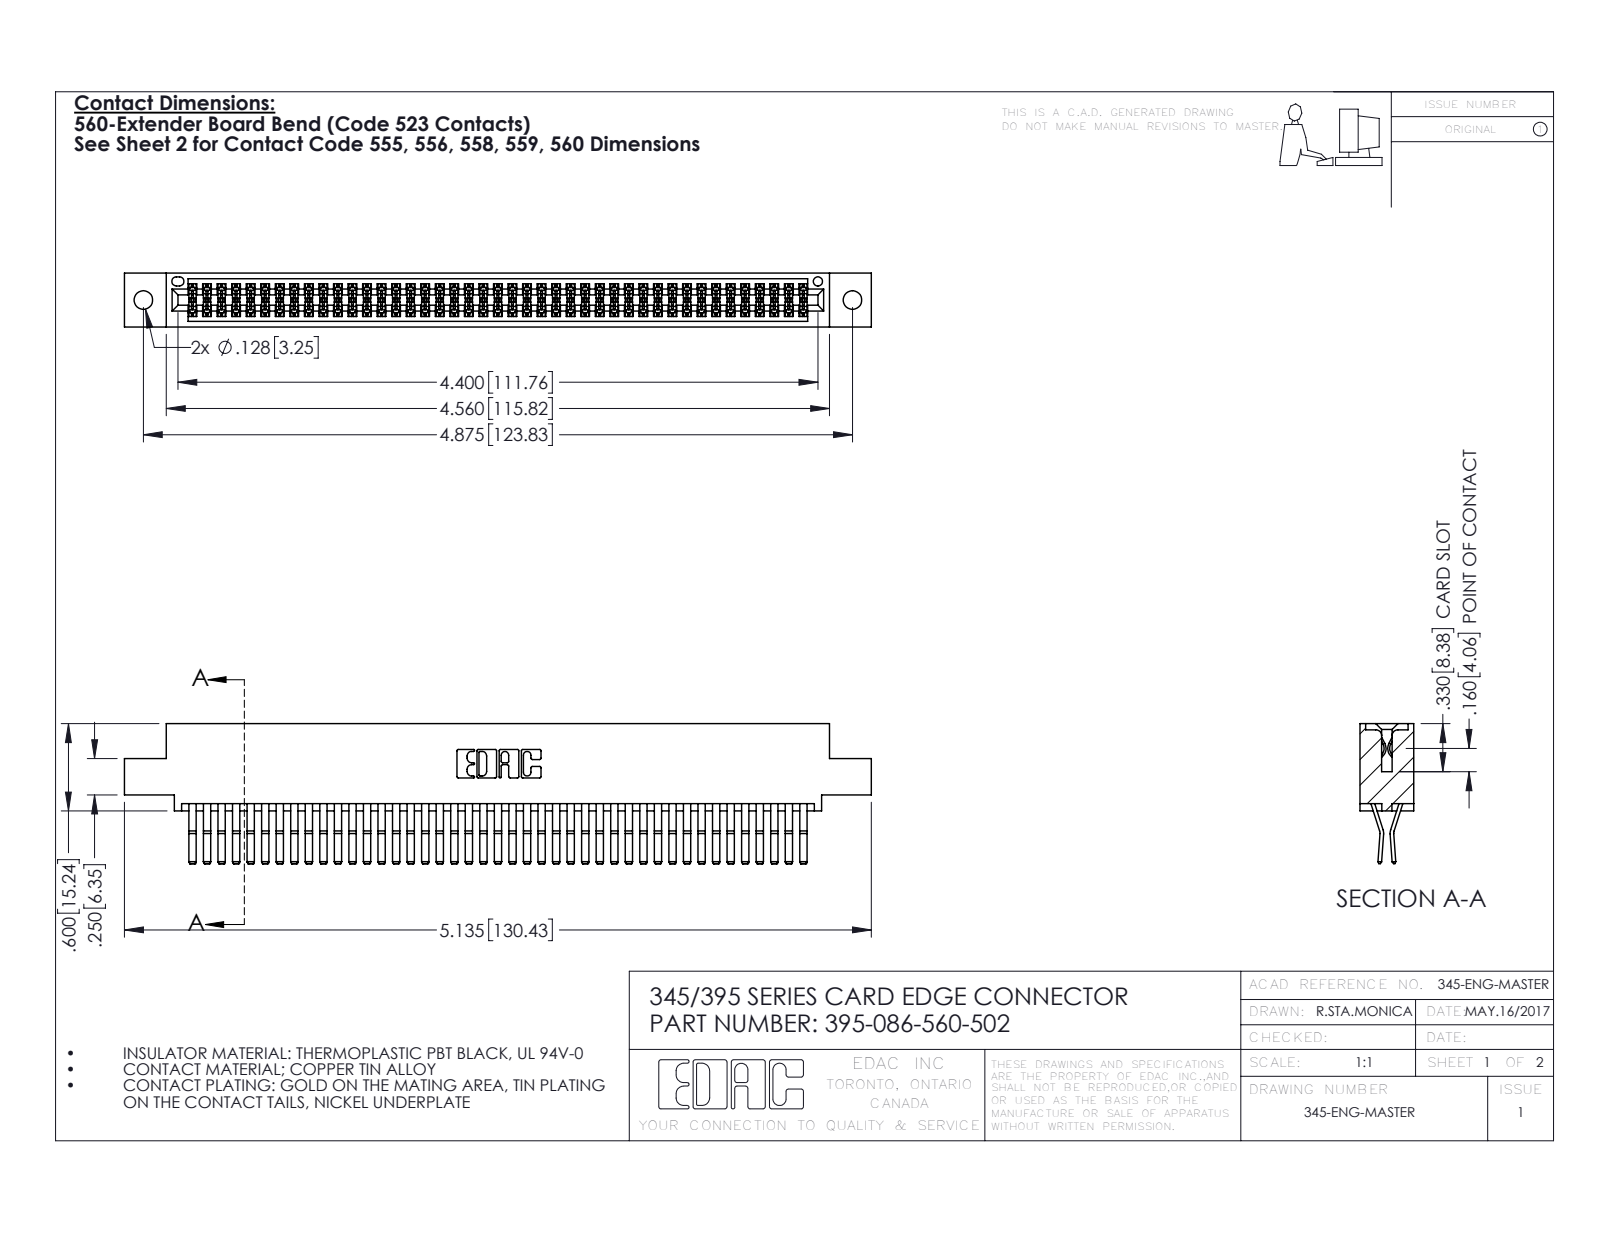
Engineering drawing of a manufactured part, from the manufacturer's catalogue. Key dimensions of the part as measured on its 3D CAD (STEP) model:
Part name (STEP PRODUCT): 395-086-560-502; 345-292-001_560 Tail; 345 Part_0.110 Offset - 0.128 Dia
STEP written by: SolidWorks 2016 (CONFIG_CONTROL_DESIGN)
Units: inches
Bodies: 87 solids, 4602 faces (2922 planar, 1680 cylindrical, 0 other)
Overall size (bounding box): 5.135 × 0.962 × 0.37
Volume: 0.801 in³ · Surface area: 32.09 in²
Round holes (diameter × count): ⌀0.128 ×2, ⌀0.064 ×1
Partial cylindrical surfaces — rounded edges, fillets, slot ends (radius × count): R0.006 ×130, R0.01 ×22, R0.007 ×6, R0.031 ×6, R0.026 ×3, R0.01 ×2, R0.014 ×2, R0.019 ×2
Main face-to-face distances: 0.025, 0.298, 0.072, 0.37, 0.2, 0.098, 0.272, 0.225, 0.175, 0.149
Hole centre spacings: 0.27, 4.639, 4.875
